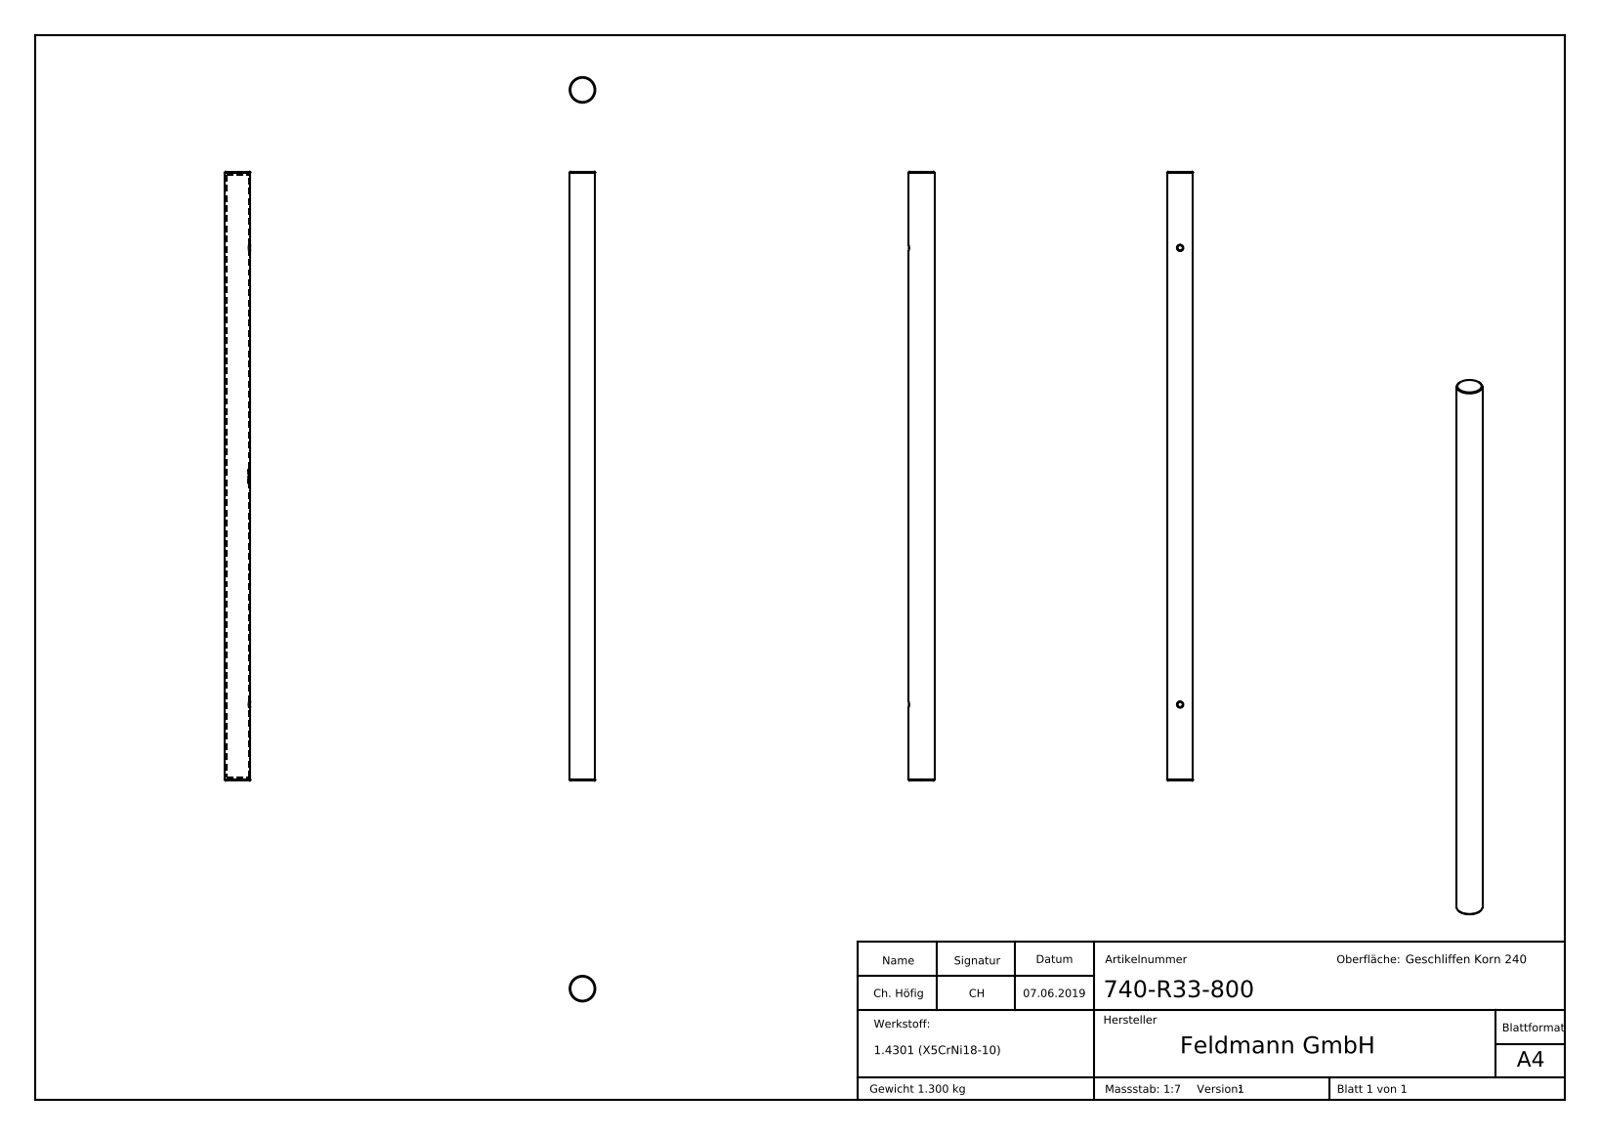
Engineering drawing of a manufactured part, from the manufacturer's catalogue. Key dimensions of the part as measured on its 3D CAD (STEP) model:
Part name (STEP PRODUCT): 740-R33-800
STEP written by: SolidWorks 2015 (CONFIG_CONTROL_DESIGN)
Units: millimetres
Bodies: 1 solid, 270 faces (105 planar, 35 cylindrical, 130 other)
Overall size (bounding box): 800 × 33.7 × 33.7
Volume: 164 619 mm³ · Surface area: 161 567 mm²
Round holes (diameter × count): ⌀6.8 ×2, ⌀29.7 ×1
Round bosses / shafts (diameter × count): ⌀33.7 ×1
Partial cylindrical surfaces — rounded edges, fillets, slot ends (radius × count): R14.95 ×1
Main face-to-face distances: 4, 796, 800, 792, 11.06, 2.02, 2.14, 10.94, 0.58, 13.08
Hole centre spacings: 600
